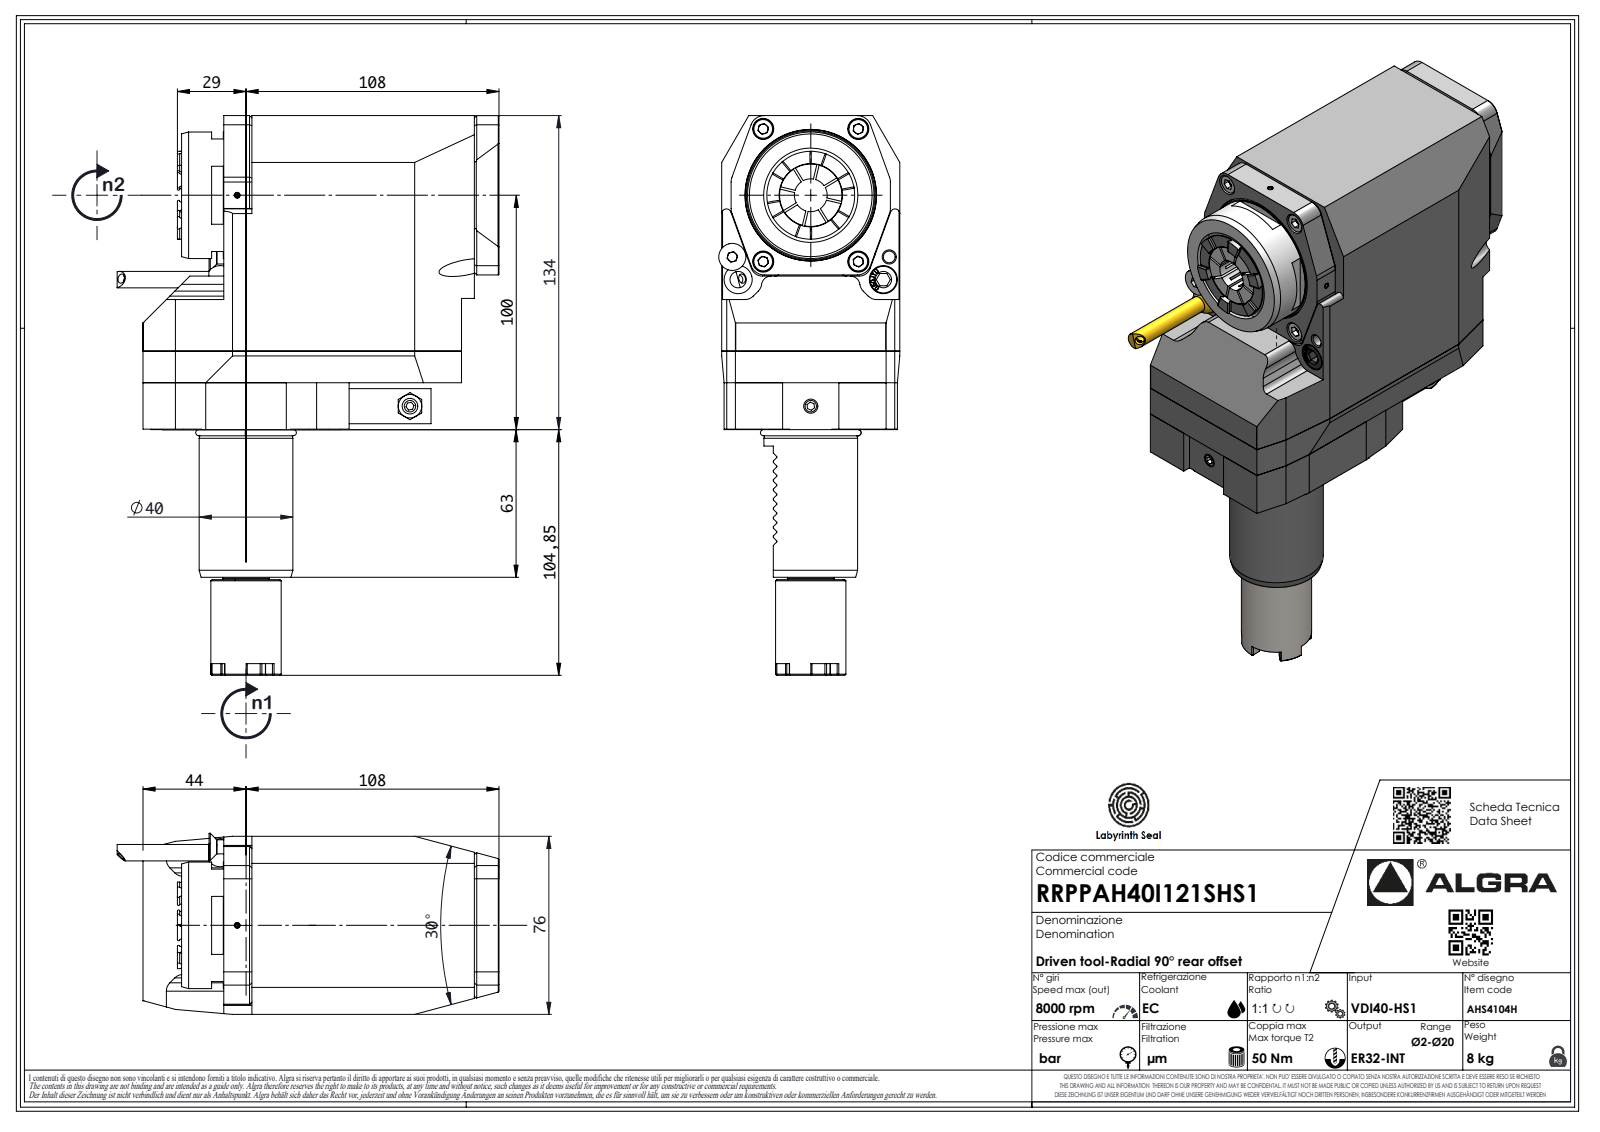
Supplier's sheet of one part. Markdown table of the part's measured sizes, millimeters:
| quantity | value |
| --- | --- |
| part name | RRPPAH40I121SHS1 |
| STEP written by | SolidWorks 2023 (AUTOMOTIVE_DESIGN) |
| units | millimeters |
| bodies | 1 solid, 656 faces (451 planar, 77 cylindrical, 128 other) |
| overall size | 238.85 × 163.5 × 76 |
| volume | 1 287 000 mm³ |
| surface area | 92 040 mm² |
| round holes (diameter × count) | 2.1 × 1, 4 × 1, 5 × 1 |
| round bosses / shafts (diameter × count) | 54 × 1, 40 × 1, 38.7 × 1, 30 × 1, 26.09 × 1, 7 × 1, 6.37 × 1, 6 × 1 |
| partial cylindrical surfaces (radius × count) | 0.3 × 10, 6 × 10, 0.33 × 7, 0.52 × 7, 3.7 × 7, 5 × 6, 2 × 3, 4 × 2 |
| main face-to-face distances | 76, 16.5, 136, 20, 134, 114, 18, 152.5, 34.5, 118 |
